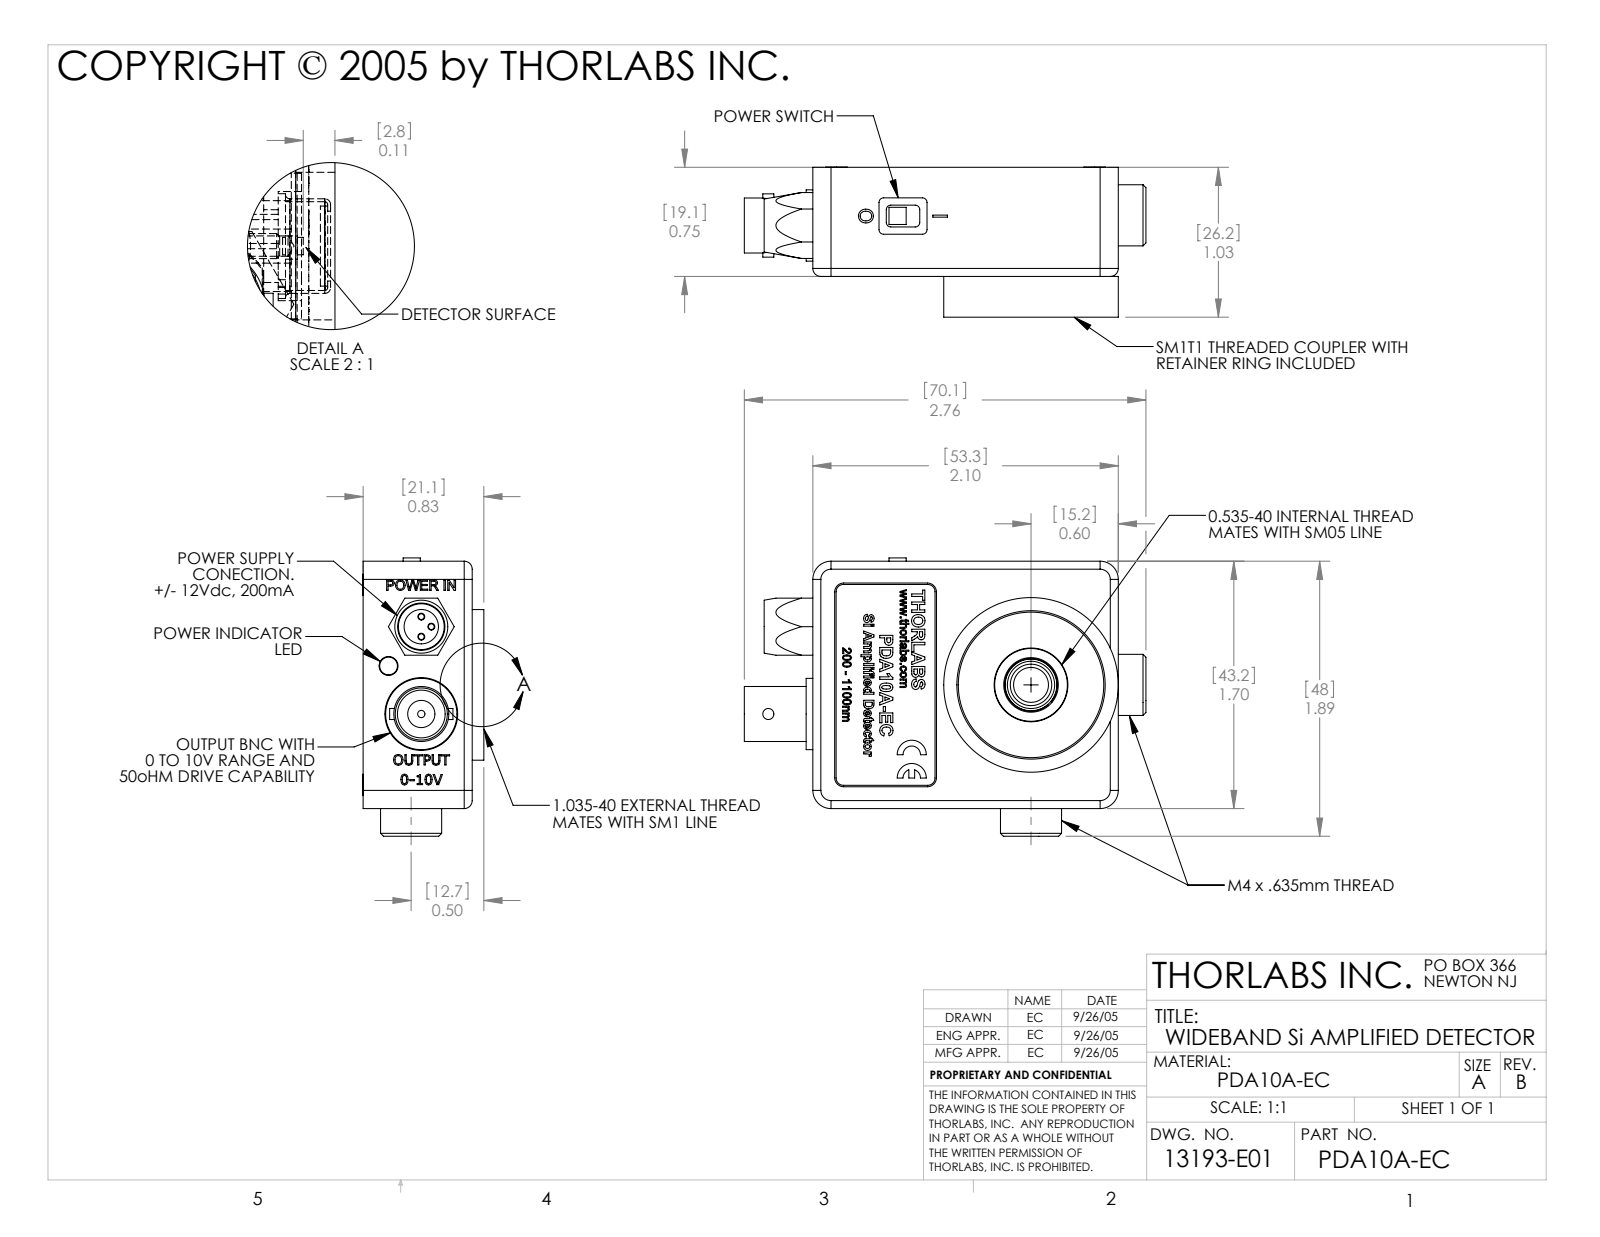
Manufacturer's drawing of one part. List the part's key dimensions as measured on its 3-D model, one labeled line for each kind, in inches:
Part name (STEP PRODUCT): 13193-E0W
STEP written by: SolidWorks 2009 (AUTOMOTIVE_DESIGN)
Units: inches
Bodies: 16 solids, 1681 faces (873 planar, 262 cylindrical, 546 other)
Overall size (bounding box): 2.761 × 1.913 × 1.031
Volume: 1.303 in³ · Surface area: 36.48 in²
Round holes (diameter × count): ⌀0.07 ×7, ⌀0.096 ×4, ⌀0.125 ×4, ⌀0.2 ×4, ⌀0.039 ×3, ⌀0.06 ×2, ⌀0.136 ×2, ⌀0.15 ×2, ⌀0.23 ×2, ⌀0.05 ×1, ⌀0.052 ×1, ⌀0.13 ×1
Round bosses / shafts (diameter × count): ⌀0.02 ×6, ⌀0.147 ×4, ⌀0.086 ×4, ⌀0.018 ×3, ⌀0.42 ×2, ⌀0.236 ×2, ⌀1.2 ×1, ⌀1.035 ×1
Partial cylindrical surfaces — rounded edges, fillets, slot ends (radius × count): R0.125 ×22, R0.031 ×8, R0.095 ×8, R0.05 ×4, R0.055 ×4, R0.063 ×4, R0.024 ×2, R0.06 ×2
Main face-to-face distances: 0.063, 0.1, 0.05, 0.07, 0.02, 0.73, 0.667, 0.68, 0.617, 0.75
Hole centre spacings: 0.069, 0.097, 0.1, 0.689, 0.736, 0.766, 0.788, 0.815
